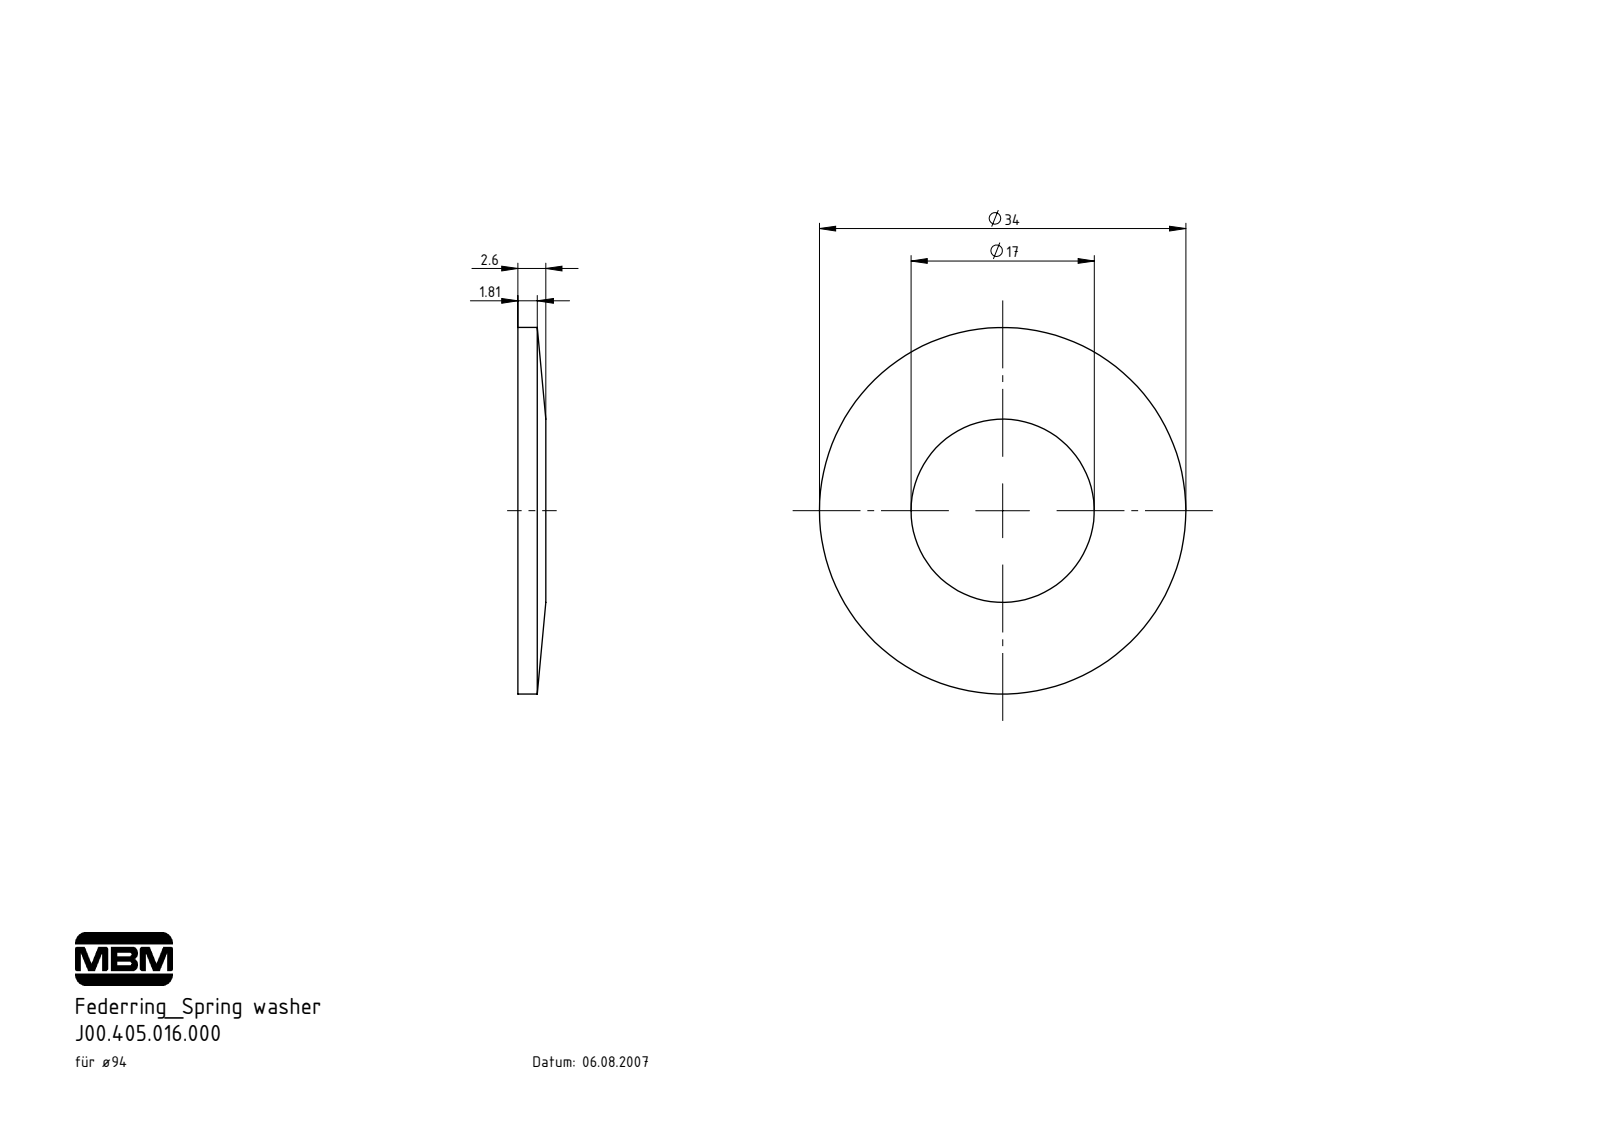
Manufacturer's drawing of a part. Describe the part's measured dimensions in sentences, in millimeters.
The part is named "J00.405.016.000". Its 3-D file was written by "SolidWorks 2022 (AUTOMOTIVE_DESIGN)". It is 1 solid with 6 faces: 2 planar, 4 cylindrical and 0 other. Overall it measures 34 by 34 by 1.8 millimeters. Its volume is 1 226 cubic millimeters and its surface area 1 650 square millimeters. Round holes: 1 of diameter 17. Round bosses or shafts: 1 of diameter 34. The main face-to-face distances are 1.8.
